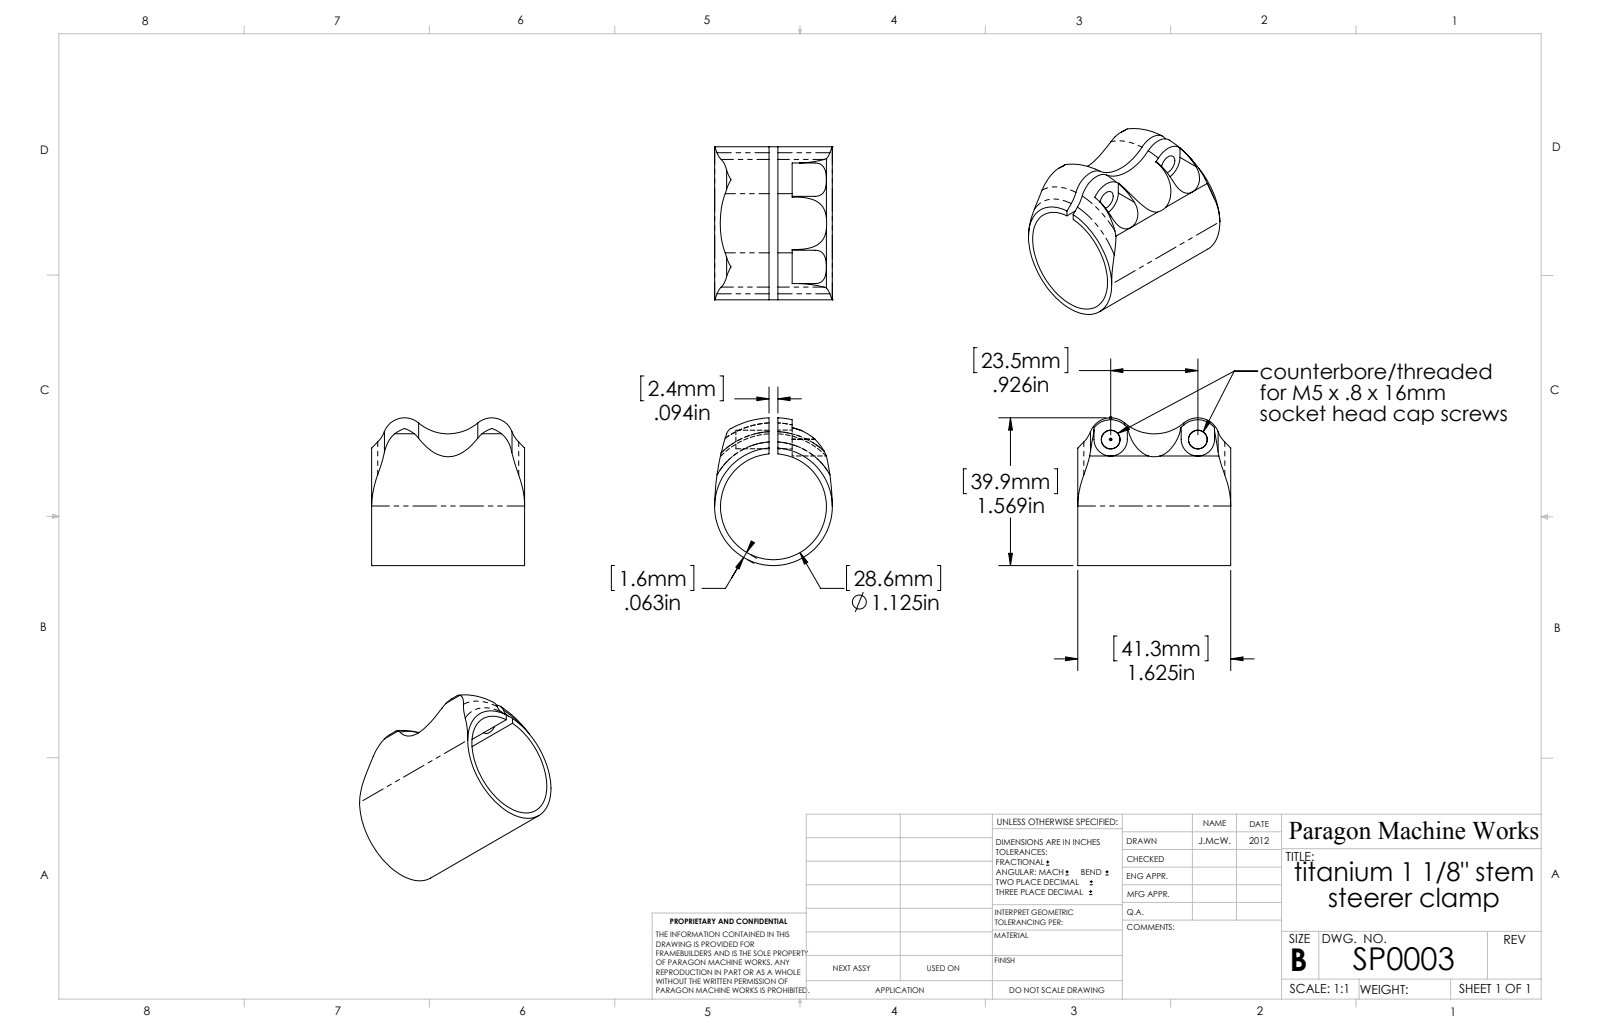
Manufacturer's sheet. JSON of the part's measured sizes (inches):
{"part_name": "SP0003", "step_written_by": "SolidWorks 2012 (AUTOMOTIVE_DESIGN)", "units": "inches", "bodies": {"solids": 1, "faces": 42, "planar": 12, "cylindrical": 16, "other": 14}, "overall_size": [1.625, 1.569, 1.25], "volume_in3": 0.714, "surface_area_in2": 15.17, "round_holes": [[0.197, 2], [0.2, 2], [1.125, 1]], "partial_cylinders_radius": [[0.177, 2], [2.554, 2], [0.1, 1], [0.5, 1], [0.625, 1]], "face_to_face_distances": [0.094, 1.625, 0.245, 0.151, 0.353, 0.447, 0.598, 0.527, 1.098, 0.172], "hole_center_spacings": [0.926]}
